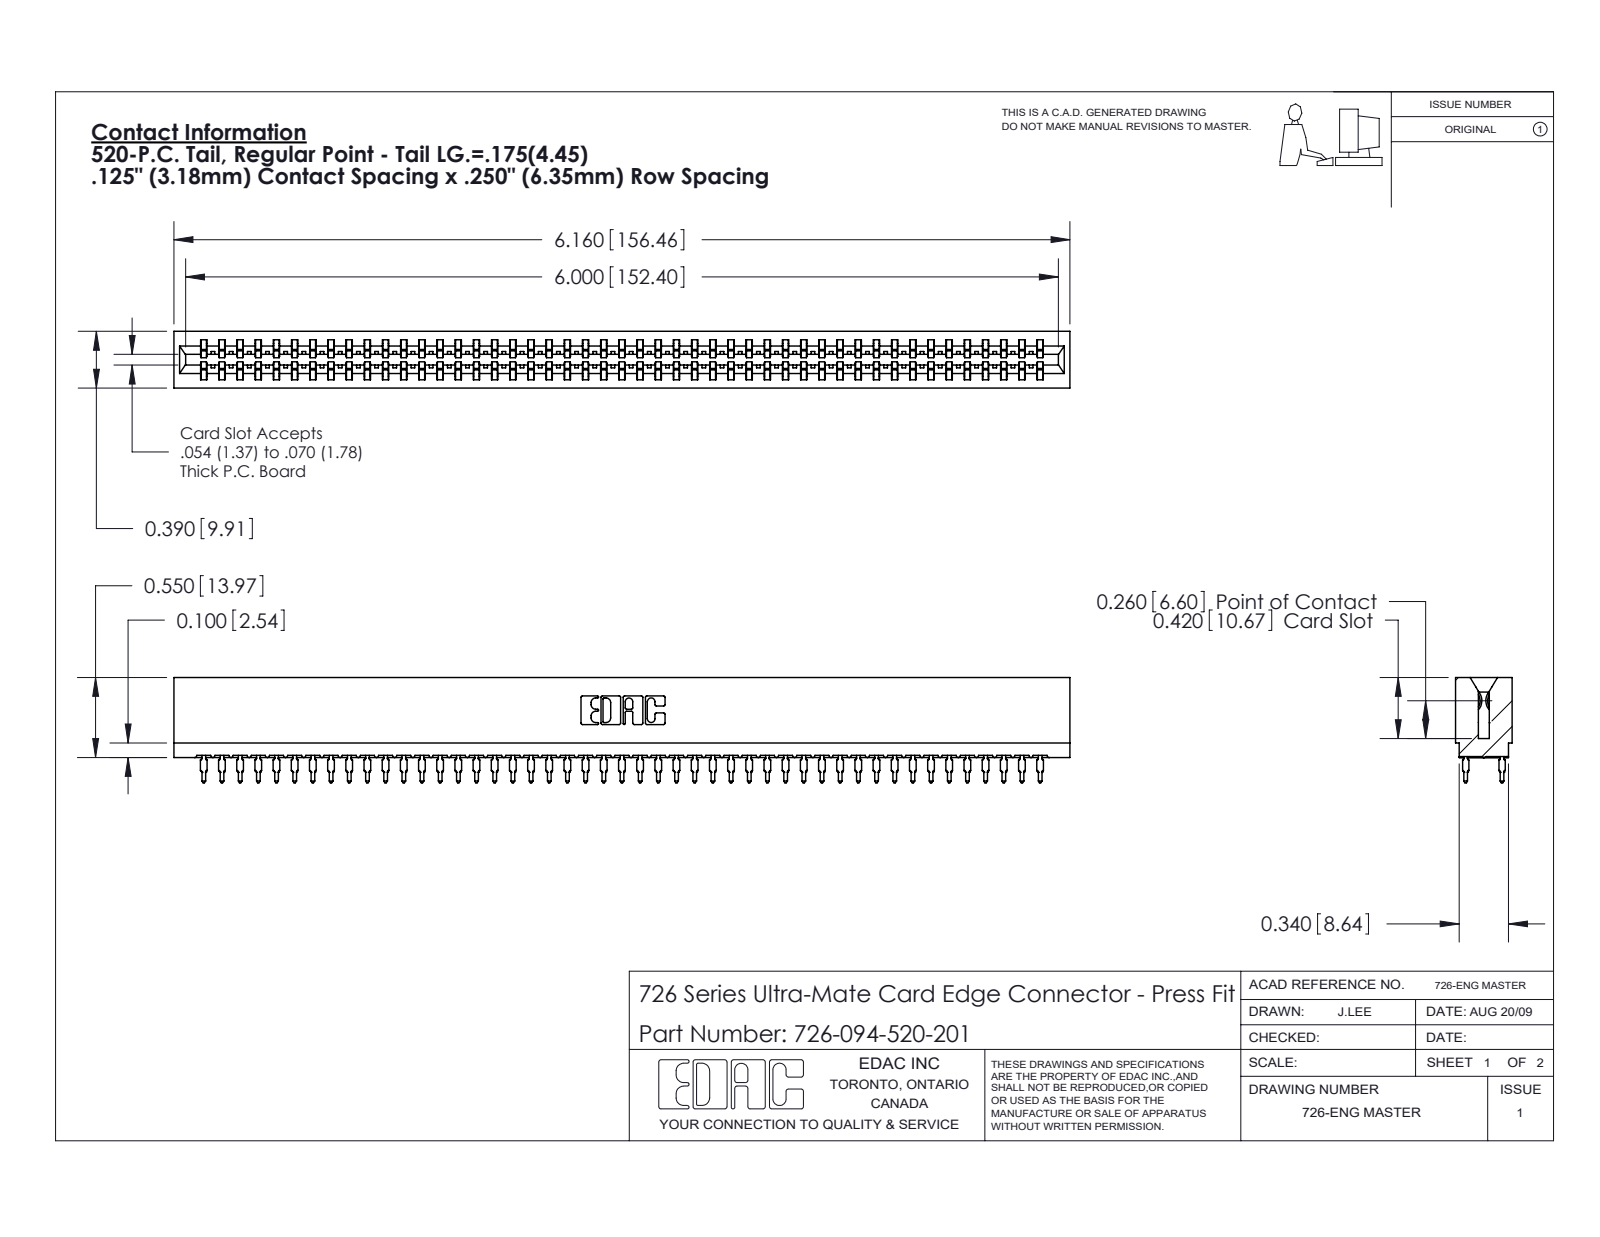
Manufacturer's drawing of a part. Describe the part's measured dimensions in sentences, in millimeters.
The part is named "746-292-001_520; 726-094-520-201; 726 Part_.515 Slot Depth - 01". Its 3-D file was written by "SolidWorks 2020 (CONFIG_CONTROL_DESIGN)". It is 95 solids with 8510 faces: 4379 planar, 1687 cylindrical and 2444 other. Overall it measures 156.5 by 18.4 by 9.9 millimeters. Its volume is 14 300 cubic millimeters and its surface area 23 500 square millimeters. Partial cylindrical surfaces (rounded edges, fillets, slot ends): 188 of radius 0.5, 48 of radius 0.4, 22 of radius 0.3, 8 of radius 0.1, 8 of radius 0.3, 6 of radius 0.2, 6 of radius 0.8, 3 of radius 0.7. The main face-to-face distances are 1.4, 8.5, 9.9, 0.6, 7.8, 6.4, 7, 2.1, 9.3, 0.8.
